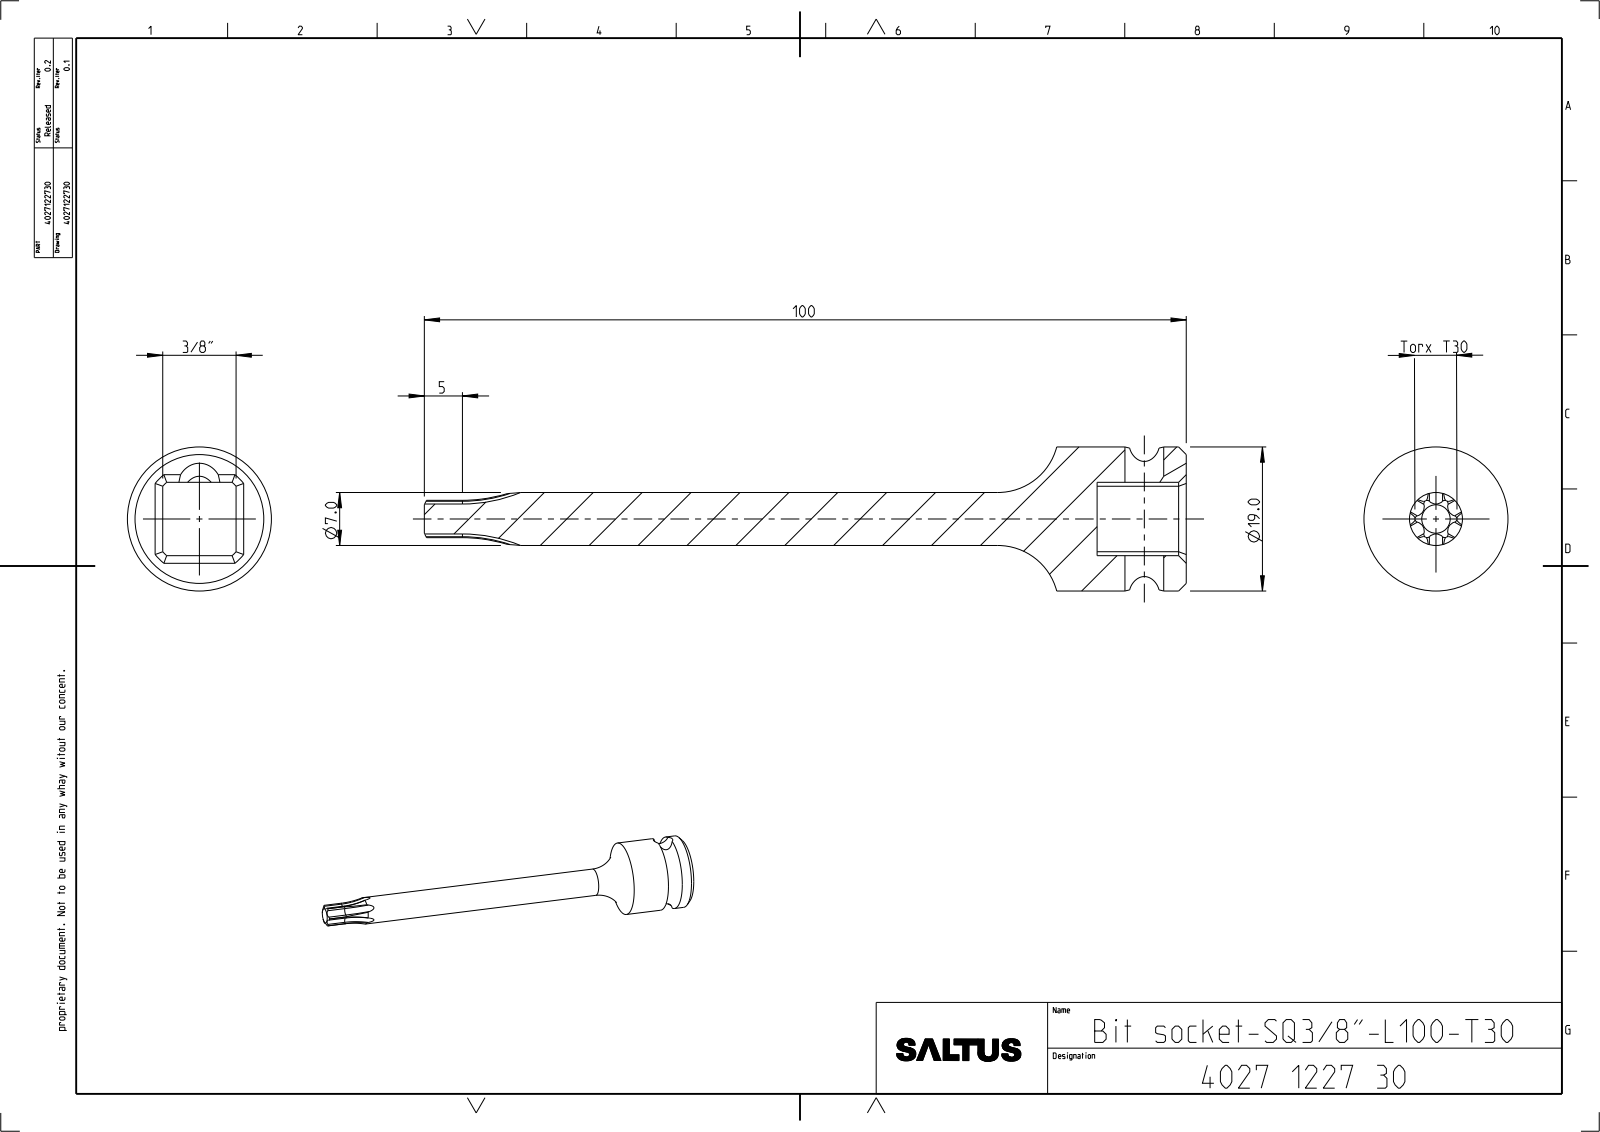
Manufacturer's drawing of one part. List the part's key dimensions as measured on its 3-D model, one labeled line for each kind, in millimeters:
Part name (STEP PRODUCT): 4027122730
STEP written by: CREO PARAMETRIC BY PTC INC, 2022414 (CONFIG_CONTROL_DESIGN)
Units: millimetres
Bodies: 1 solid, 87 faces (12 planar, 39 cylindrical, 36 other)
Overall size (bounding box): 100 × 18.9 × 18.9
Volume: 6 571 mm³ · Surface area: 3 748 mm²
Round holes (diameter × count): ⌀5.09 ×1
Round bosses / shafts (diameter × count): ⌀18.9 ×1, ⌀6.95 ×1
Partial cylindrical surfaces — rounded edges, fillets, slot ends (radius × count): R0.42 ×12, R1.22 ×6, R2.76 ×1, R3 ×1, R6.45 ×1
Main face-to-face distances: 9.62, 11.7, 100, 88.3
